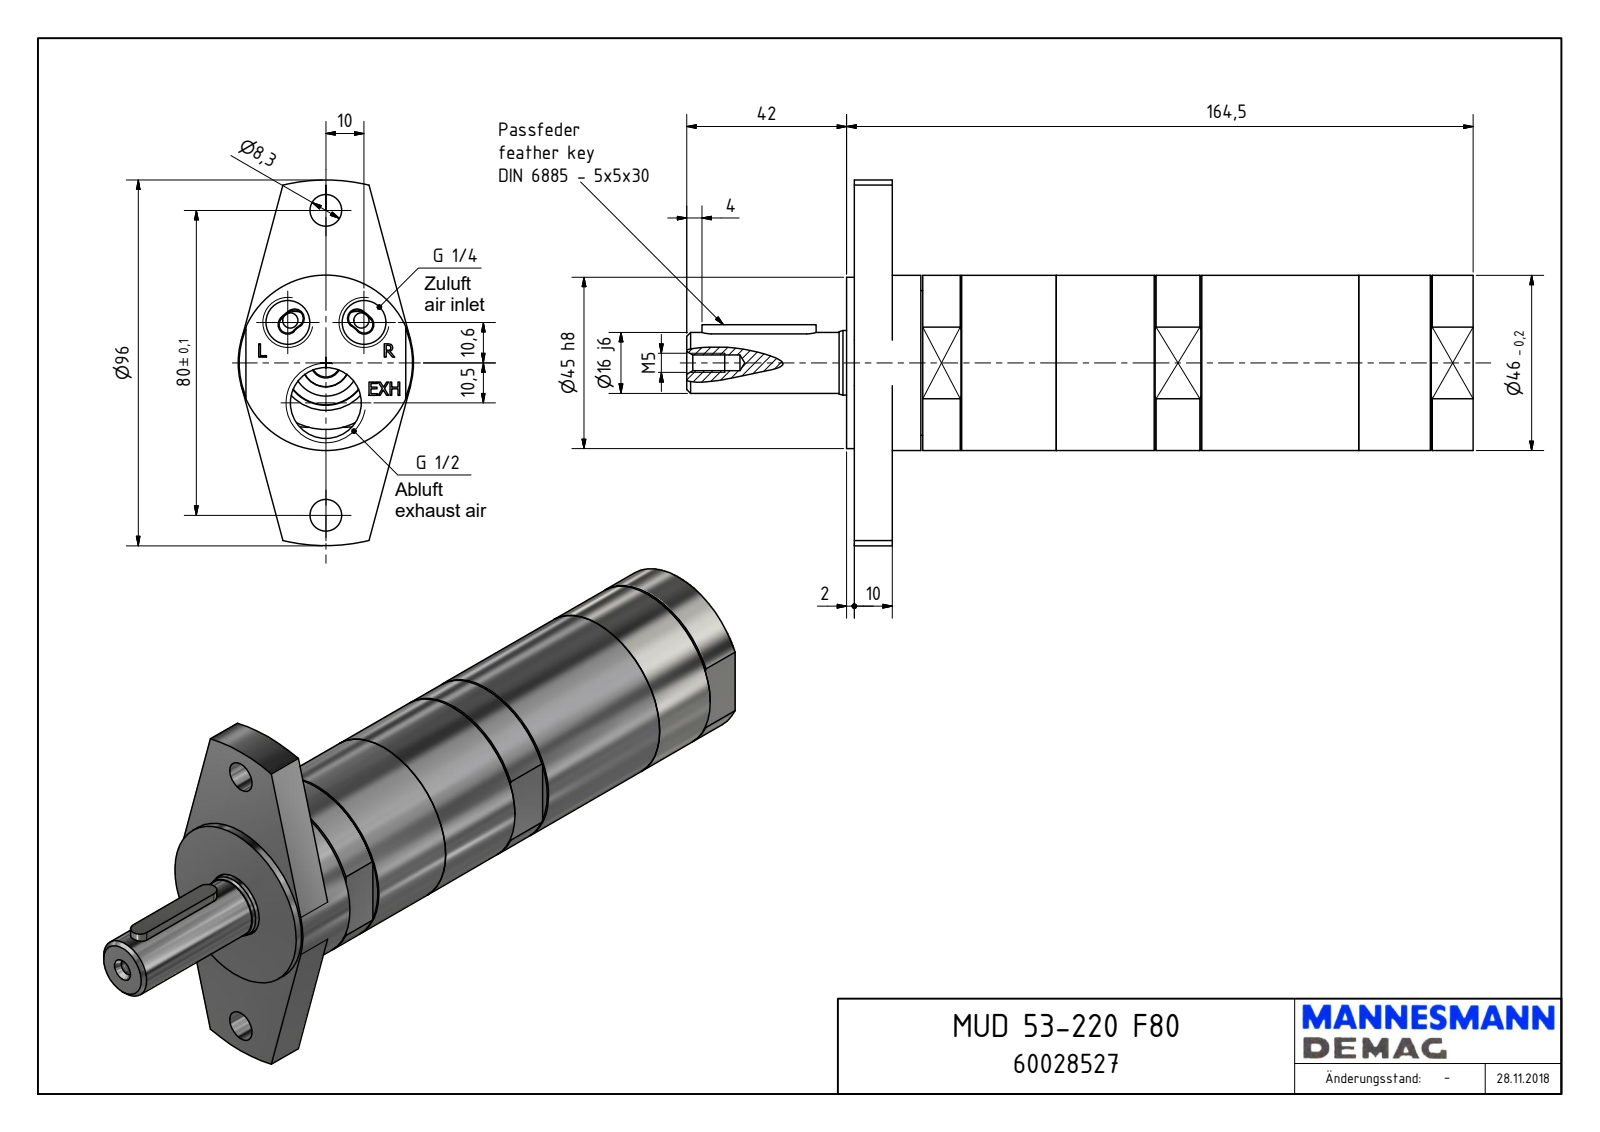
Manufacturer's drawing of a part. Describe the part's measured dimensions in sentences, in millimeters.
The part is named "MUD 53-220 F80_60028527". Its 3-D file was written by "Autodesk Inventor 2018 (AUTOMOTIVE_DESIGN)". It is 1 solid with 176 faces: 104 planar, 38 cylindrical and 34 other. Overall it measures 206.5 by 96 by 46 millimeters. Its volume is 290 911 cubic millimeters and its surface area 38 608 square millimeters. Round holes: 2 of diameter 8.3, 2 of diameter 11.45, 1 of diameter 4.13, 1 of diameter 17.5, 1 of diameter 18.63, 1 of diameter 21.5, 1 of diameter 23, 1 of diameter 38, 1 of diameter 38.38. Round bosses or shafts: 1 of diameter 46, 1 of diameter 45, 1 of diameter 19.56, 1 of diameter 16.95, 1 of diameter 16. Partial cylindrical surfaces (rounded edges, fillets, slot ends): 2 of radius 2.5, 2 of radius 5, 1 of radius 17.61, 1 of radius 48. The main face-to-face distances are 10, 12, 2, 164.5, 162.5, 152.5, 42, 8, 144.5, 18. The hole center spacings are 14.57, 23.35, 31.05, 40, 51.58, 10.5, 20, 29.5.
